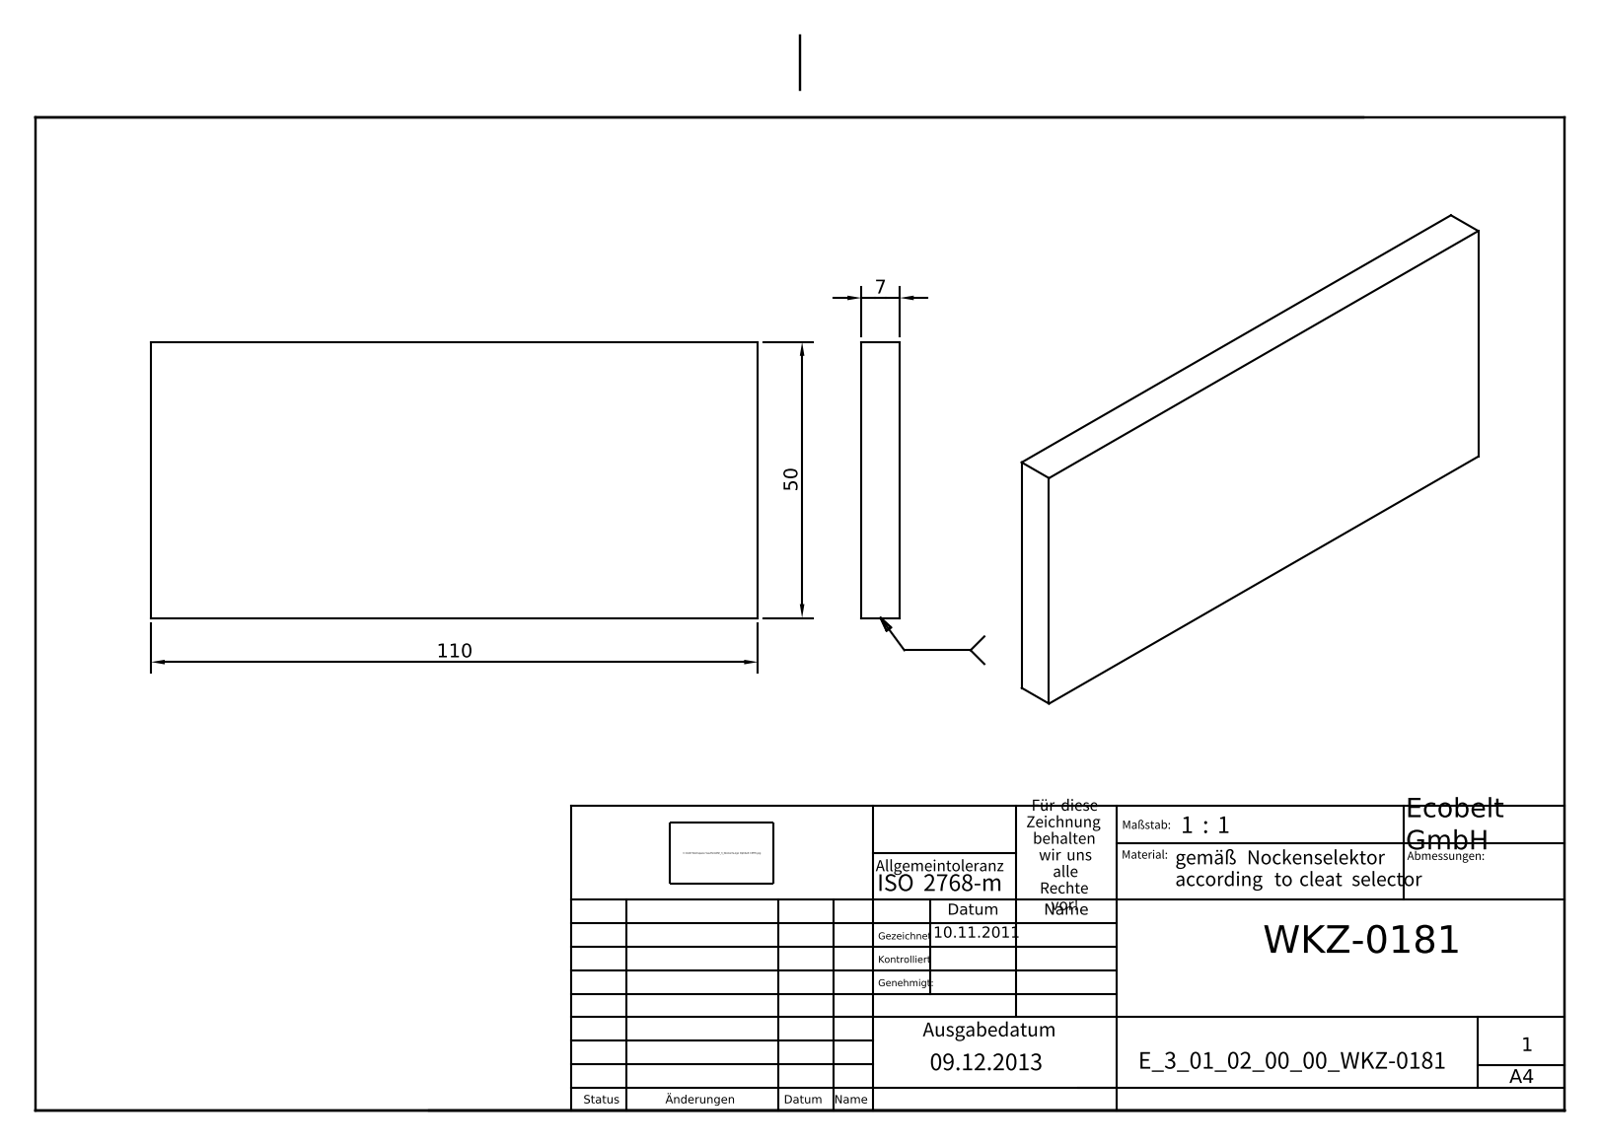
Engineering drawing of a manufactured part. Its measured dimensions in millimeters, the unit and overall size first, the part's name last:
Units: millimetres
Overall size (bounding box): 110 × 50 × 7
Main face-to-face distances: 7, 50, 110
Volume: 38 500 mm³ · Surface area: 13 240 mm²
Bodies: 1 solid, 6 faces (6 planar, 0 cylindrical, 0 other)
Part name (STEP PRODUCT): E_3_01_02_00_00_WKZ-0181
STEP written by: Autodesk Inventor 2021 (AUTOMOTIVE_DESIGN)
